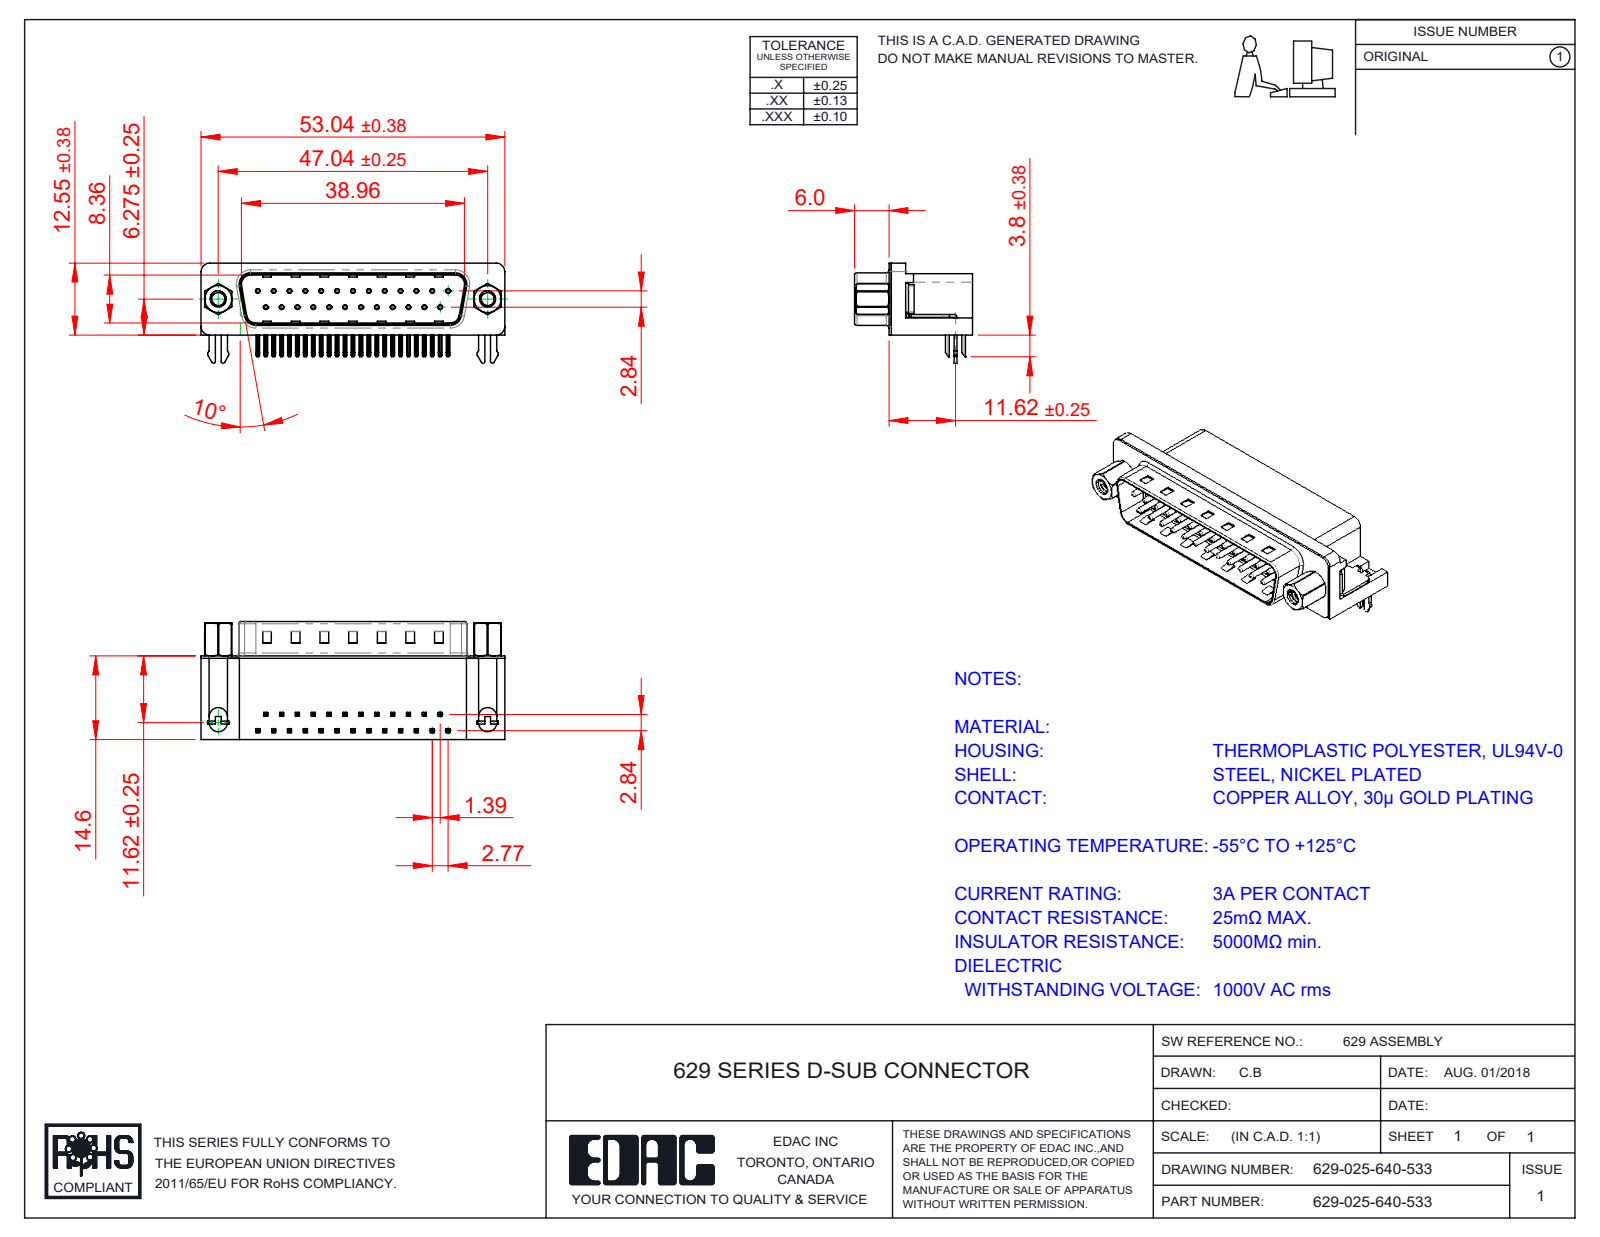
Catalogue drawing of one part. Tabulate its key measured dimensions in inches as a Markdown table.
| quantity | value |
| --- | --- |
| part name | 629-025-640-533; 629 Housing_25 Socket; 629 Shell_25 Socket; 629 Contact Bottom (+4 more) |
| STEP written by | SolidWorks 2020 (CONFIG_CONTROL_DESIGN) |
| units | inches |
| bodies | 33 solids, 2427 faces (1457 planar, 739 cylindrical, 231 other) |
| overall size | 2.088 × 0.811 × 0.688 |
| volume | 0.46 in³ |
| surface area | 13.54 in² |
| round holes (diameter × count) | 0.014 × 25, 0.031 × 25, 0.089 × 2, 0.09 × 2, 0.157 × 2, 0.189 × 2, 0.197 × 2 |
| round bosses / shafts (diameter × count) | 0.03 × 25, 0.193 × 2, 0.187 × 2, 0.154 × 2, 0.11 × 2 |
| partial cylindrical surfaces (radius × count) | 0.01 × 108, 0.005 × 50, 0.039 × 16, 0.02 × 14, 0.063 × 8, 0.059 × 7, 0.013 × 4, 0.035 × 4 |
| main face-to-face distances | 0.016, 0.408, 0.559, 0.083, 0.345, 0.575, 0.067, 0.412, 0.428, 0.461 |
| hole center spacings | 0.124, 0.109, 0.218, 0.327, 0.436, 0.545, 0.654, 0.198 |
